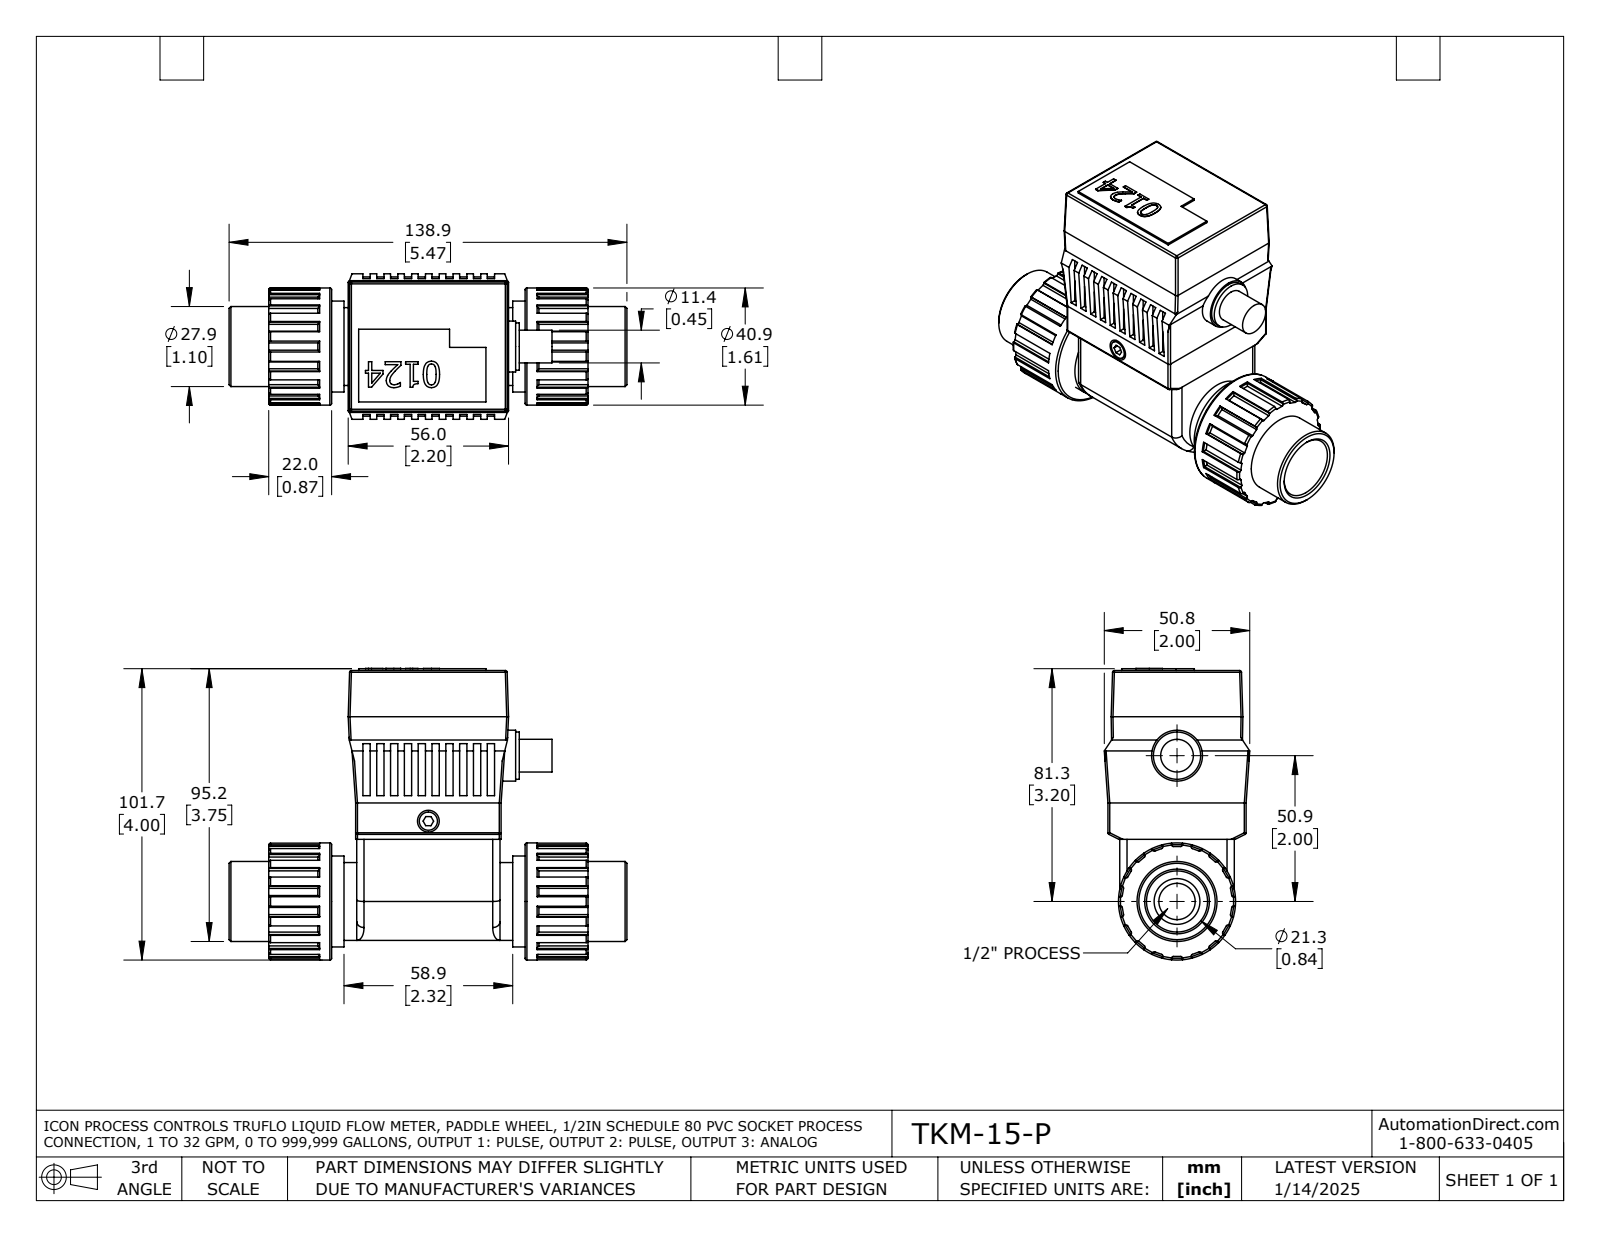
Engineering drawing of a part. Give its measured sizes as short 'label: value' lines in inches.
name: TKM-15-P
written by: SolidWorks 2021 (AUTOMOTIVE_DESIGN)
unit: in
bodies: 9 solids, 744 faces (375 planar, 236 cylindrical, 133 other)
size: 5.47 × 4.008 × 2
volume: 15.9 in³; area: 99.35 in²
holes: 4× ⌀0.128, 2× ⌀1.1, 1× ⌀0.3, 1× ⌀0.5, 1× ⌀0.63, 1× ⌀0.84, 1× ⌀0.95, 1× ⌀1.177, 1× ⌀1.2
bosses: 1× ⌀1.61, 1× ⌀1.25, 1× ⌀1.18, 1× ⌀1.07, 1× ⌀1.024, 1× ⌀0.85, 1× ⌀0.7, 1× ⌀0.65
rounds: 98× R0.025, 4× R0.1, 1× R0.465, 1× R0.512, 1× R0.847
face distances: 0.75, 2.32, 0.865, 1.195, 3.195, 2.75, 0.445, 3.945, 0.345, 3.18
hole spacings: 0.979, 1.181, 1.561, 1.957
